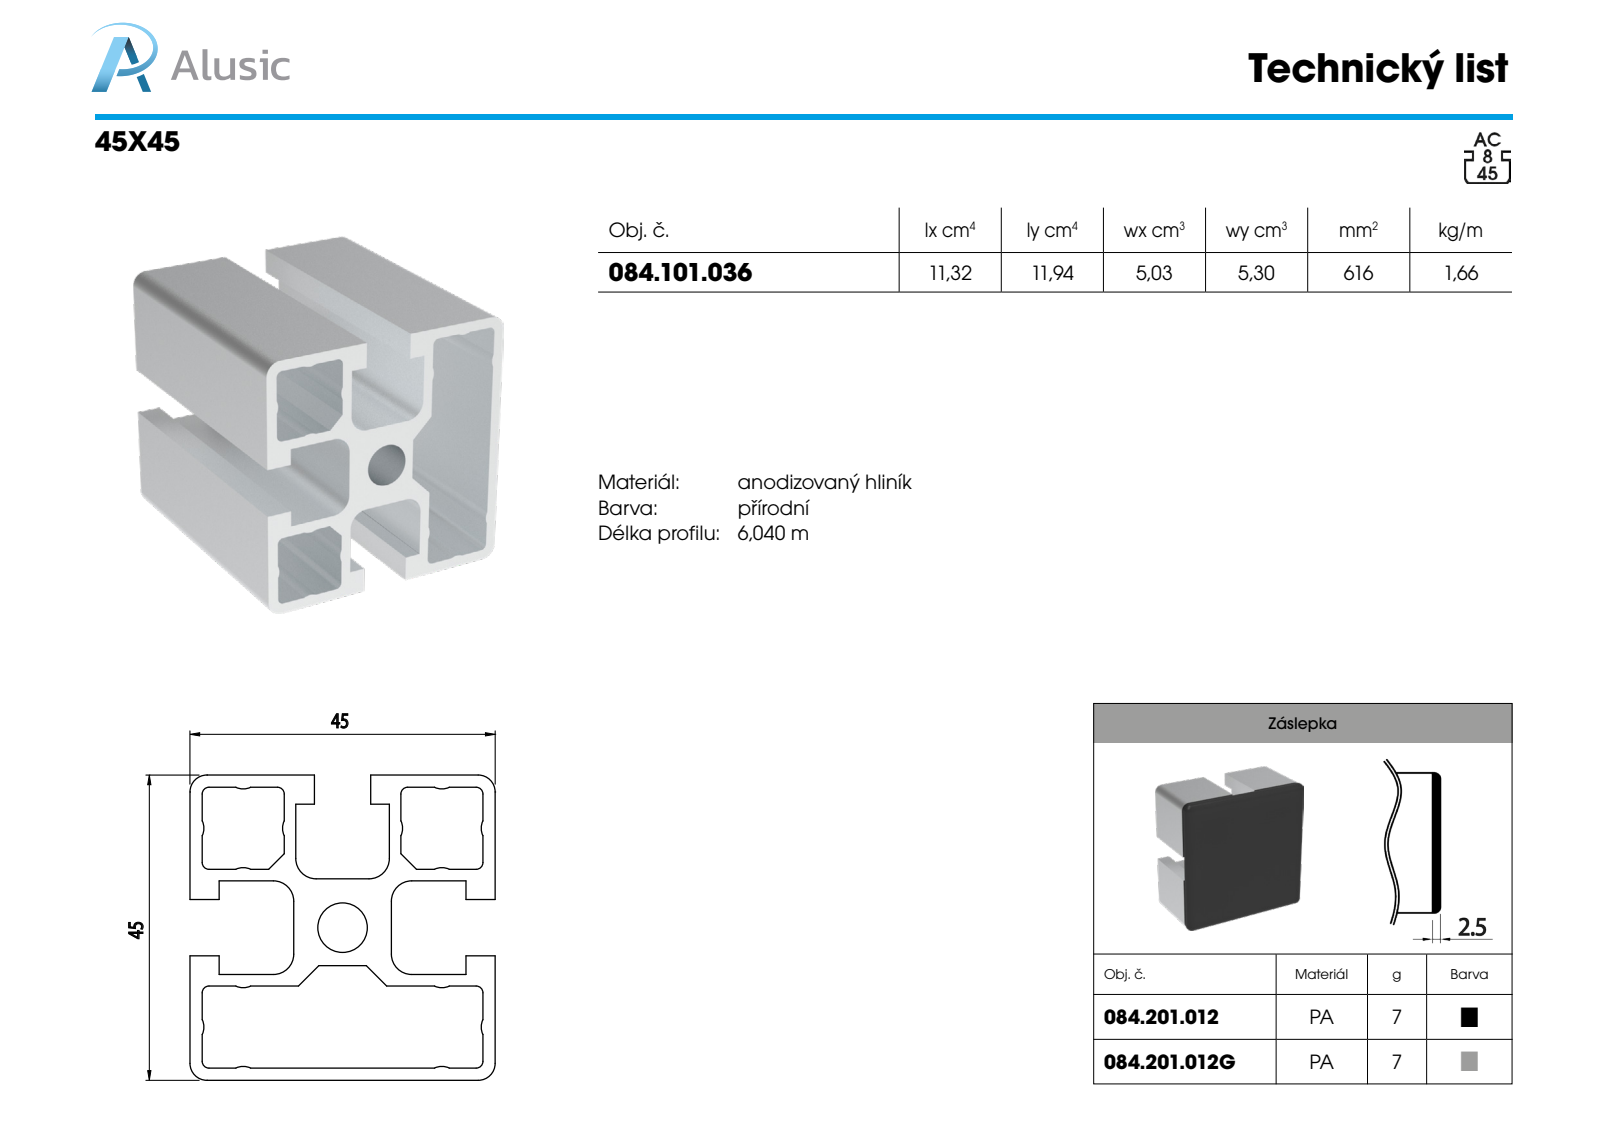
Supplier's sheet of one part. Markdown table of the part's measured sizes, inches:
| quantity | value |
| --- | --- |
| part name | 084.101.036 |
| STEP written by | SolidWorks 2018 (AUTOMOTIVE_DESIGN) |
| units | inches |
| bodies | 1 solid, 102 faces (62 planar, 40 cylindrical, 0 other) |
| overall size | 3.937 × 1.772 × 1.772 |
| volume | 3.715 in³ |
| surface area | 81.94 in² |
| round holes (diameter × count) | 0.287 × 1 |
| partial cylindrical surfaces (radius × count) | 0.098 × 18, 0.039 × 10, 0.118 × 6 |
| main face-to-face distances | 0.071, 1.701, 0.543, 1.772, 0.614, 1.157, 1.087, 0.547, 1.224, 0.476 |
